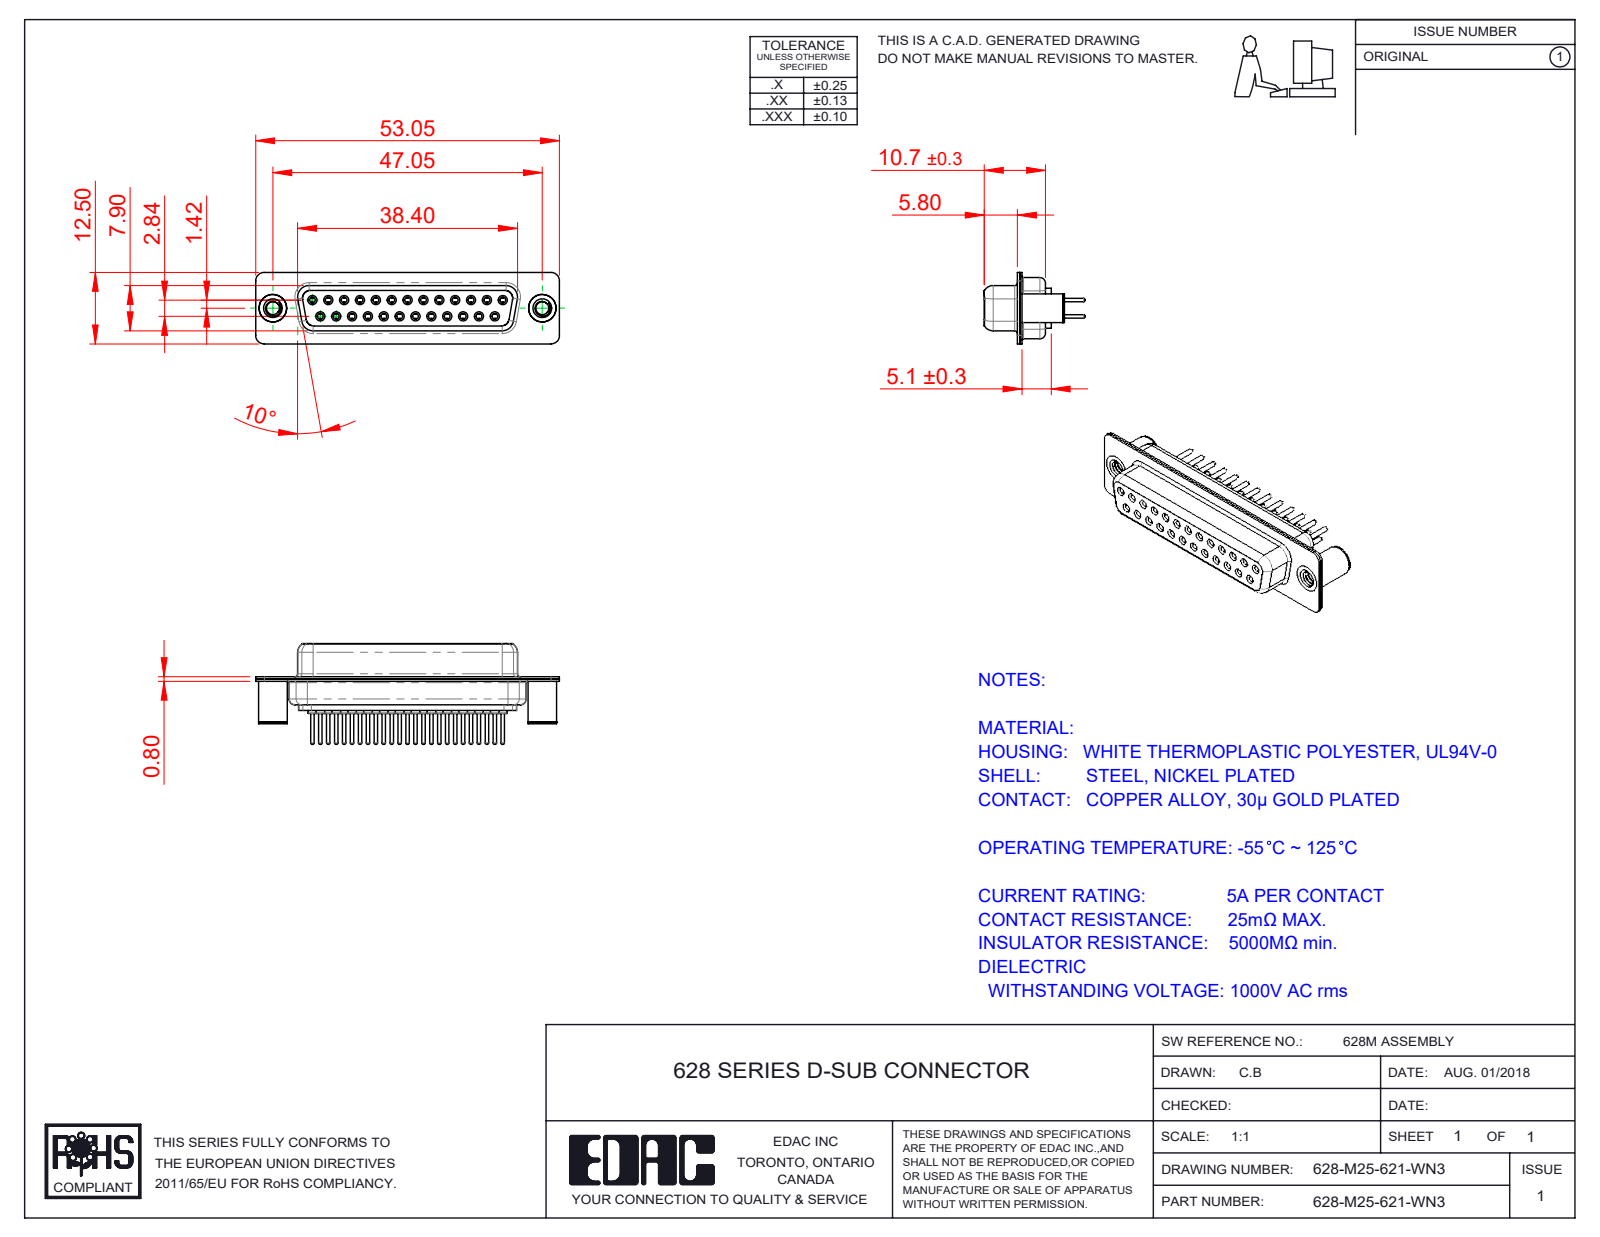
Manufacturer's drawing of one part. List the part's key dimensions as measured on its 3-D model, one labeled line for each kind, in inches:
Part name (STEP PRODUCT): 628M Housing_25 Contacts; 628M Contact Row 2_21; 628-M25-621-WN3; 628M Shell Rear_25 Contacts (+3 more)
STEP written by: SolidWorks 2020 (CONFIG_CONTROL_DESIGN)
Units: inches
Bodies: 30 solids, 1688 faces (442 planar, 636 cylindrical, 610 other)
Overall size (bounding box): 2.089 × 0.693 × 0.492
Volume: 0.236 in³ · Surface area: 14.58 in²
Round holes (diameter × count): ⌀0.039 ×25, ⌀0.043 ×25, ⌀0.067 ×25, ⌀0.071 ×25, ⌀0.079 ×25, ⌀0.089 ×2, ⌀0.128 ×2, ⌀0.157 ×2, ⌀0.189 ×2
Round bosses / shafts (diameter × count): ⌀0.087 ×25, ⌀0.063 ×25, ⌀0.059 ×25, ⌀0.024 ×25, ⌀0.197 ×2, ⌀0.193 ×2
Partial cylindrical surfaces — rounded edges, fillets, slot ends (radius × count): R0.059 ×16, R0.079 ×12, R0.053 ×8, R0.063 ×8, R0.01 ×4, R0.02 ×4, R0.024 ×4, R0.026 ×4
Main face-to-face distances: 0.016, 0.055, 0.018, 0.333, 0.35, 0.071, 0.244, 0.278, 0.039, 0.073
Hole centre spacings: 0.124, 0.109, 0.218, 0.327, 0.436, 0.545, 0.198, 0.295
